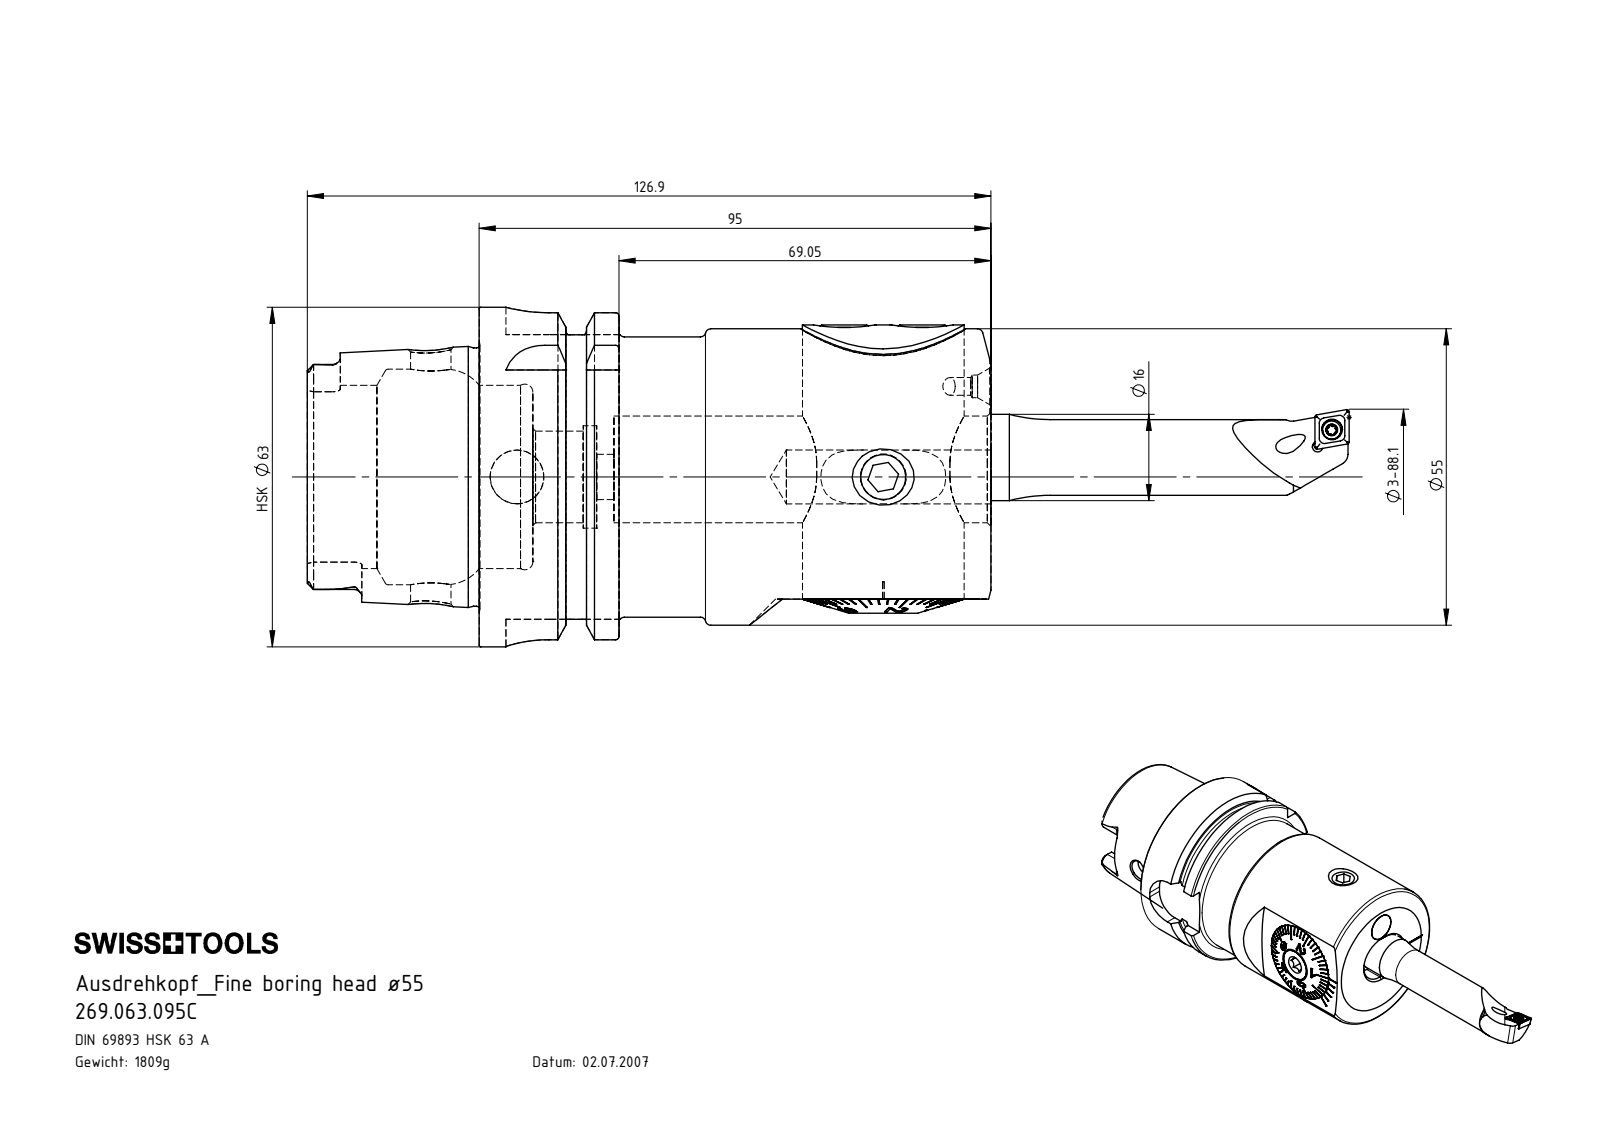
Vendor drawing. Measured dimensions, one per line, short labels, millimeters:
name: A55-BG2.011.016_E; HA6-A55.K00.095_B_Fertigbearbeitung; ISO 4026 - M10 x 16_PreviewCfg; DIN 3771 - 25x1.5 (+8 more)
written by: SolidWorks 2017 (CONFIG_CONTROL_DESIGN)
unit: mm
bodies: 17 solids, 947 faces (374 planar, 201 cylindrical, 372 other)
size: 193.39 × 63 × 63
volume: 230 685 mm³; area: 62 302 mm²
holes: 3× ⌀8.5, 2× ⌀2, 2× ⌀3, 2× ⌀10, 1× ⌀1, 1× ⌀1.6, 1× ⌀2.05, 1× ⌀2.8, 1× ⌀3.3, 1× ⌀3.85, 1× ⌀4.2, 1× ⌀7.5
bosses: 3× ⌀10, 1× ⌀63, 1× ⌀55, 1× ⌀54.95, 1× ⌀52, 1× ⌀47.93, 1× ⌀30, 1× ⌀29.98
rounds: 6× R0.21, 6× R0.34, 6× R0.59, 6× R1.4, 5× R0.36, 4× R2.88, 4× R8, 3× R3.2
face distances: 95, 6.8, 16, 25.95, 69.05, 4, 2.8, 2.5, 9.95, 85.05
hole spacings: 7.25, 14.5, 3.63, 4.05, 4.15, 14.95, 15.67, 18.83
